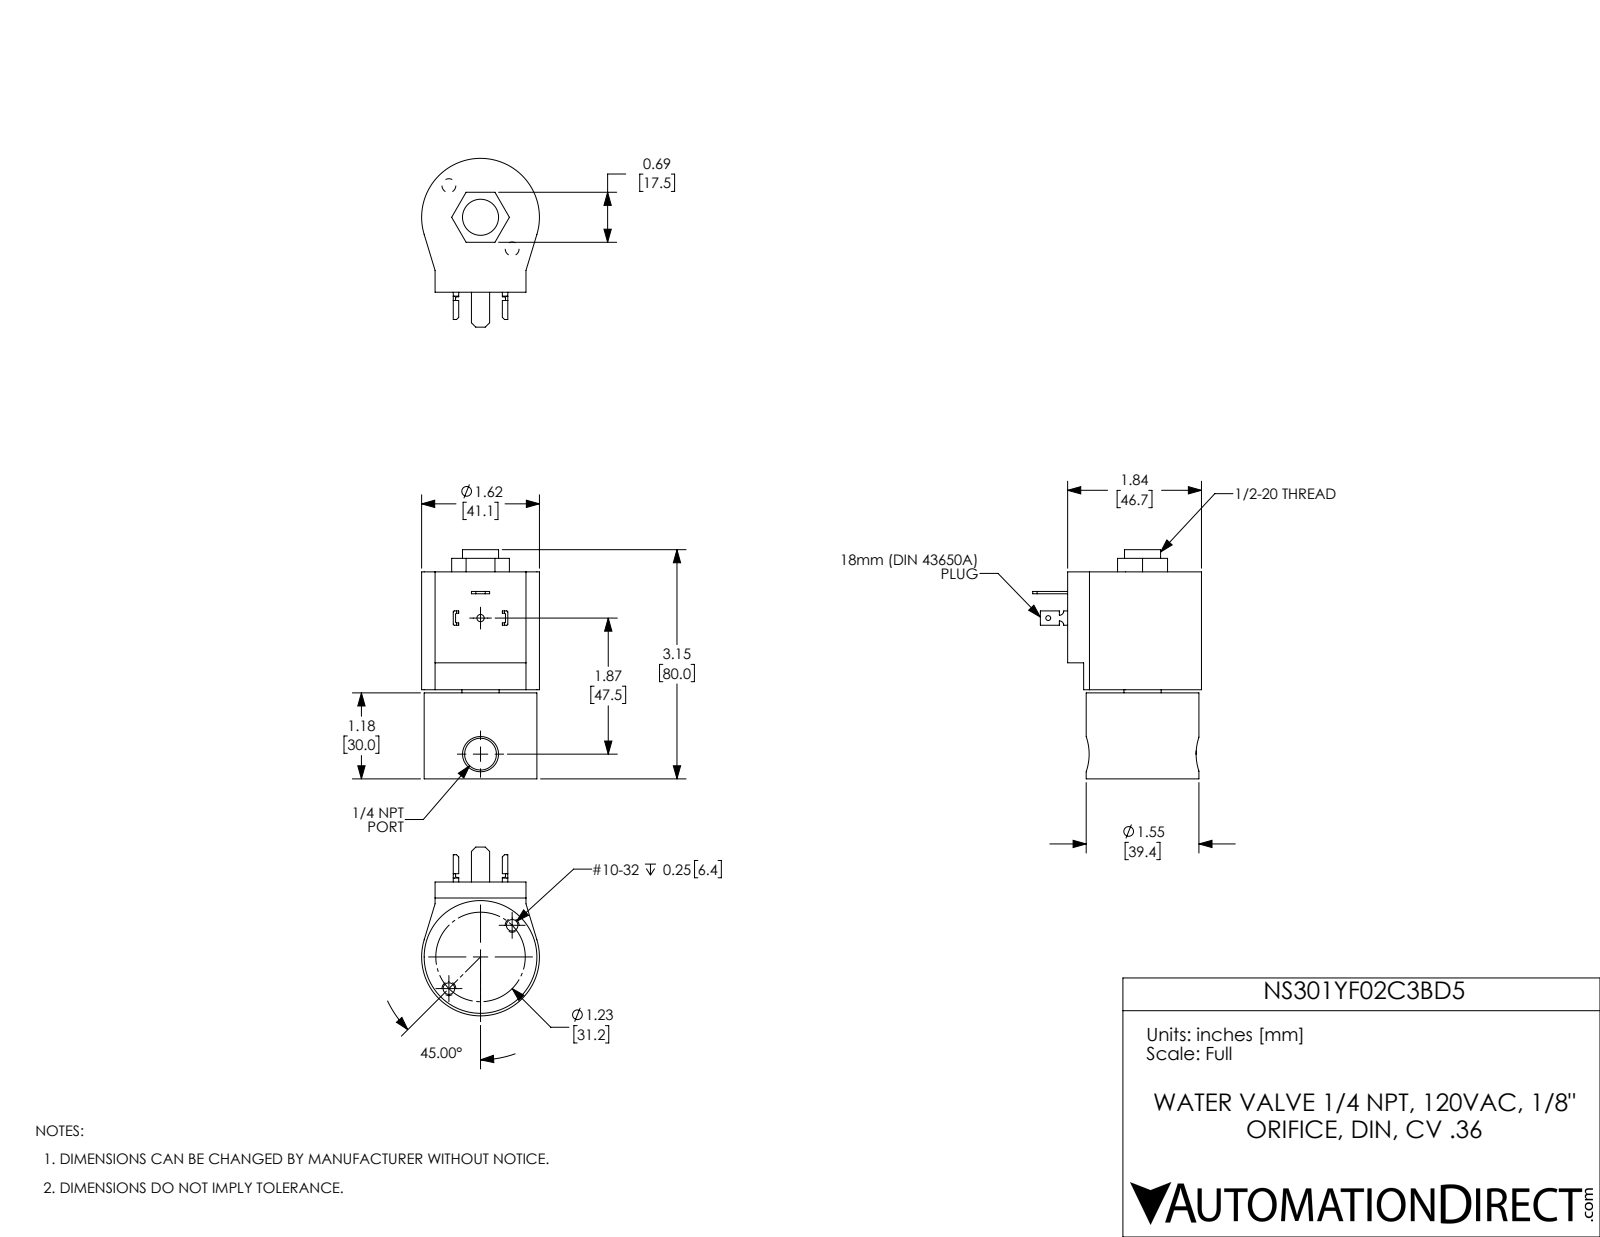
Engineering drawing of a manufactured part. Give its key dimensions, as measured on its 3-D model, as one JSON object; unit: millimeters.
{"part_name": "NS301YF02C3BD5", "step_written_by": "SolidWorks 2017 (AUTOMOTIVE_DESIGN)", "units": "millimeters", "bodies": {"solids": 6, "faces": 130, "planar": 73, "cylindrical": 49, "other": 8}, "overall_size": [80, 58.9, 41.1], "volume_mm3": 98760, "surface_area_mm2": 21340, "round_holes": [[4, 2], [1.7, 1], [2.5, 1], [11.1, 1], [12.6, 1], [13, 1], [29.3, 1]], "round_bosses_or_shafts": [[39.4, 1]], "partial_cylinders_radius": [[0.4, 8], [1.5, 2], [20.6, 1]], "face_to_face_distances": [72.3, 30, 42.2, 31.1, 1.1, 41.1, 32.7, 2.7, 1.6, 39.6], "hole_center_spacings": [15.6, 31.2, 47.5]}
